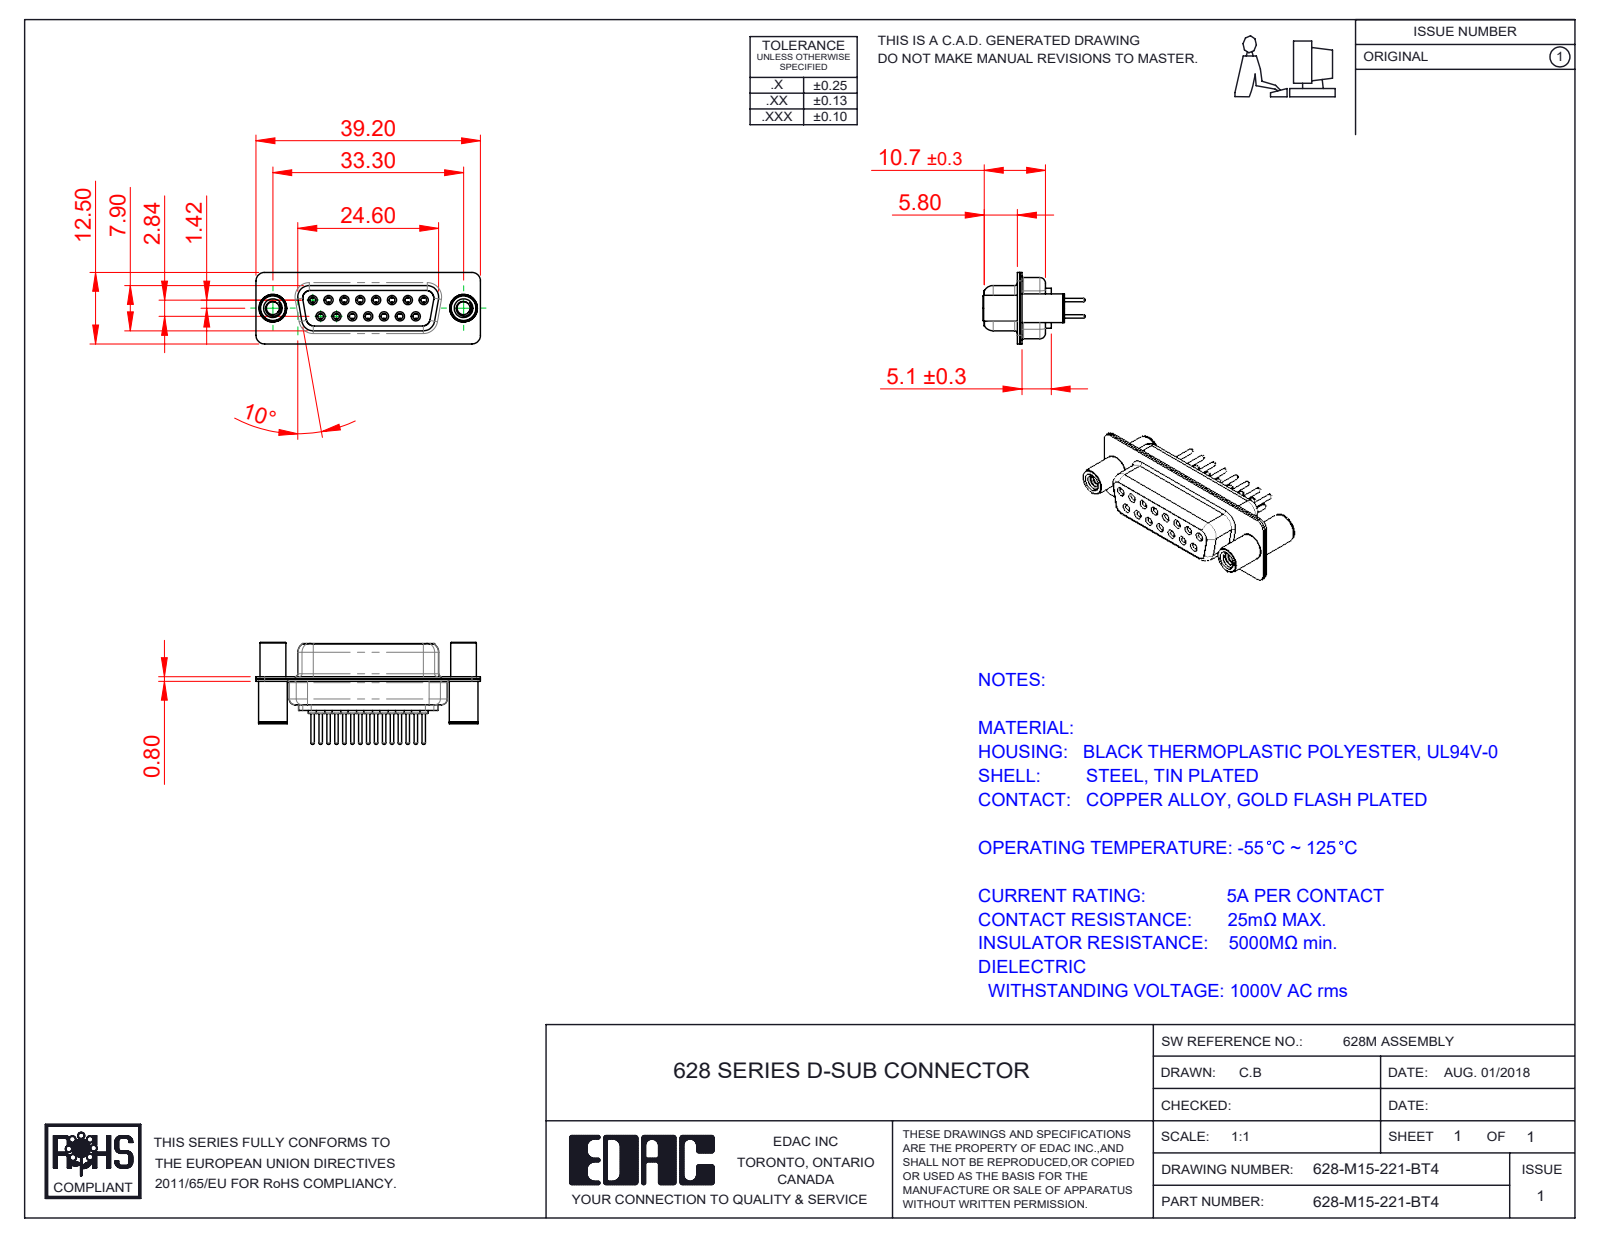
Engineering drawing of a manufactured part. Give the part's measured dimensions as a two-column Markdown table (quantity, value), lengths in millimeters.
| quantity | value |
| --- | --- |
| part name | 628-M15-221-BT4; 628M Contact Row 2_21; 628M Shell Rear_15 Contacts; 628M Housing_15 Contacts (+3 more) |
| STEP written by | SolidWorks 2020 (CONFIG_CONTROL_DESIGN) |
| units | millimeters |
| bodies | 20 solids, 1190 faces (298 planar, 474 cylindrical, 418 other) |
| overall size | 39.2 × 17.8 × 12.5 |
| volume | 2 759 mm³ |
| surface area | 6 729 mm² |
| round holes (diameter × count) | 1 × 15, 1.1 × 15, 1.7 × 15, 1.8 × 15, 2 × 15, 2.26 × 2, 3.26 × 2, 4 × 2, 4.8 × 2 |
| round bosses / shafts (diameter × count) | 2.2 × 15, 1.6 × 15, 1.5 × 15, 0.6 × 15, 5 × 2, 4.9 × 2, 4.5 × 2 |
| partial cylindrical surfaces (radius × count) | 1.5 × 16, 2 × 12, 1.35 × 8, 1.6 × 8, 0.25 × 4, 0.5 × 4, 0.6 × 4, 0.65 × 4 |
| main face-to-face distances | 0.4, 1.4, 0.45, 8.45, 1.8, 8.9, 6.2, 7.05, 1, 1.85 |
| hole center spacings | 3.16, 2.77, 5.54, 8.31, 11.08, 5.03, 5.04, 7.48 |
